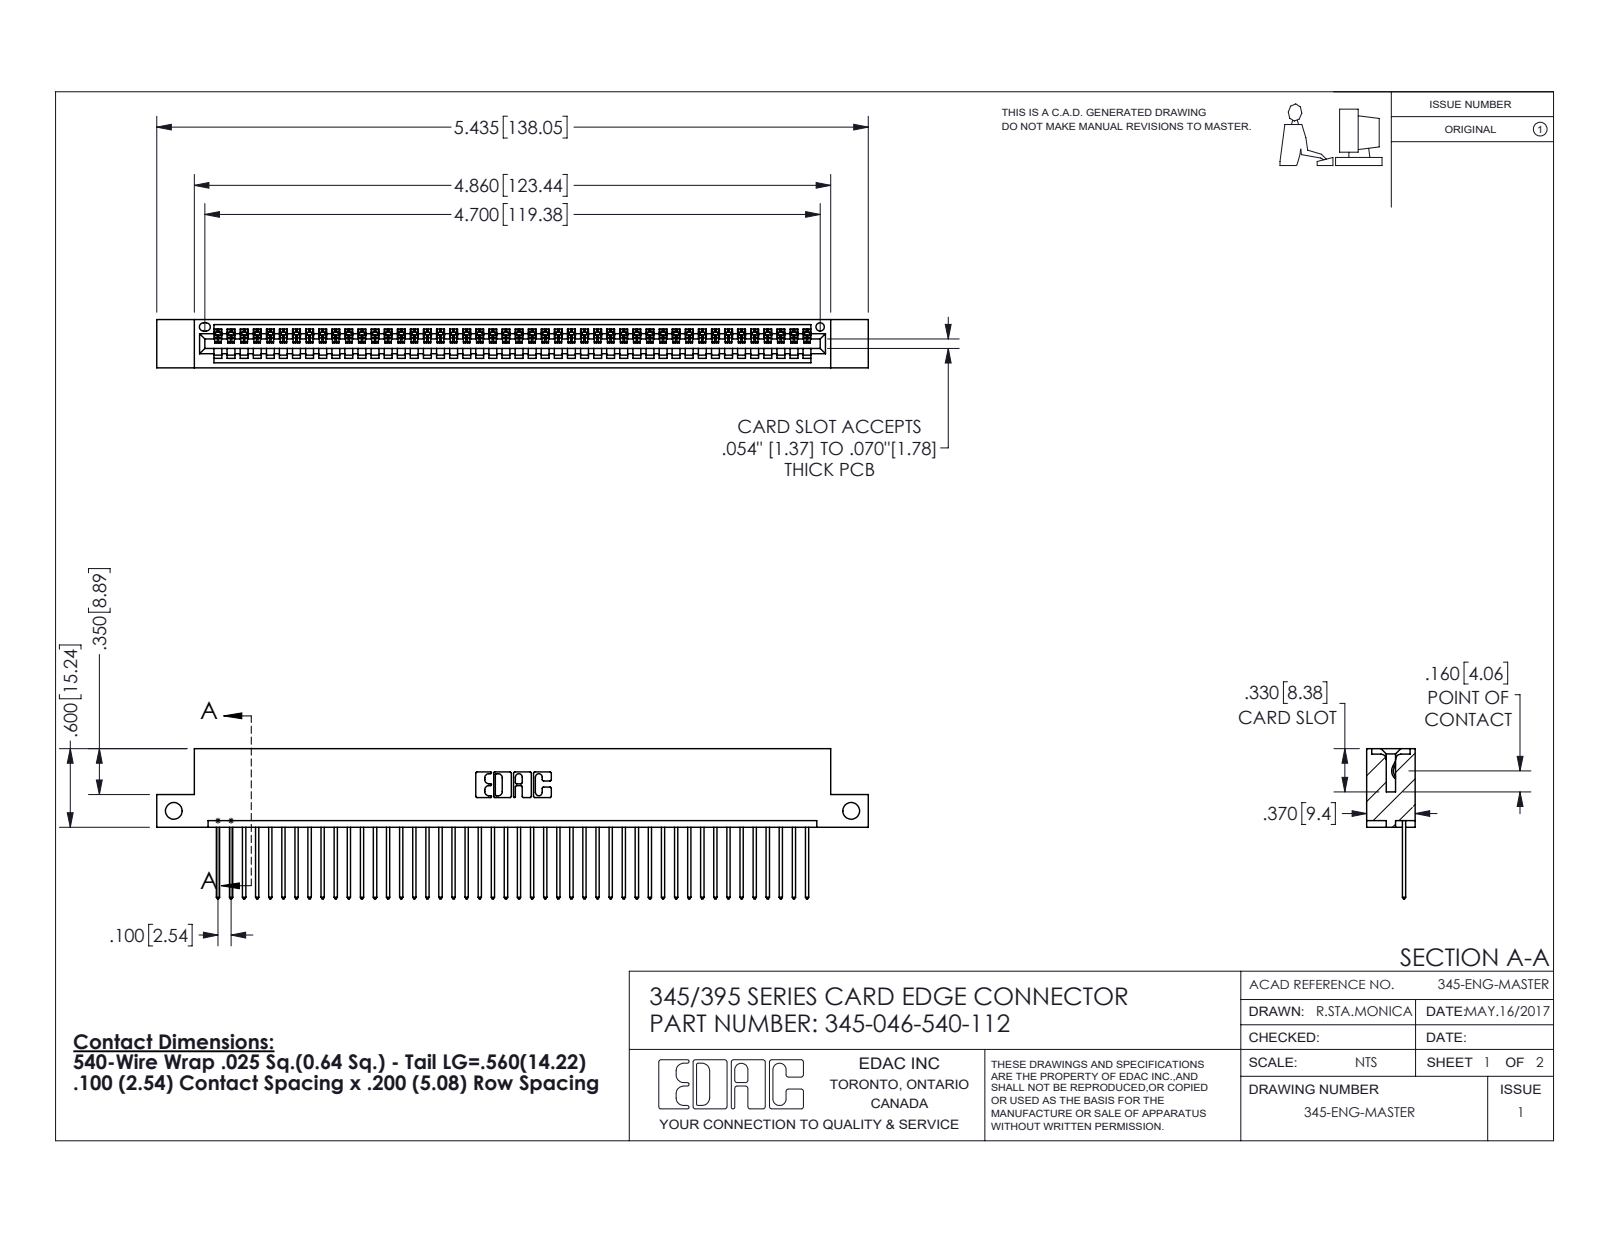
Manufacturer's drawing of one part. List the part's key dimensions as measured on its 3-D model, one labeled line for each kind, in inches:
Part name (STEP PRODUCT): 345-292-001_345-293-140; 345-046-540-112; 345 Part_Flush Mounting Lugs - Side Mount
STEP written by: SolidWorks 2016 (CONFIG_CONTROL_DESIGN)
Units: inches
Bodies: 47 solids, 2794 faces (1920 planar, 874 cylindrical, 0 other)
Overall size (bounding box): 5.435 × 1.147 × 0.37
Volume: 0.801 in³ · Surface area: 27.58 in²
Round holes (diameter × count): ⌀0.128 ×2, ⌀0.064 ×1
Partial cylindrical surfaces — rounded edges, fillets, slot ends (radius × count): R0.006 ×92, R0.01 ×92, R0.01 ×22, R0.007 ×6, R0.031 ×6, R0.026 ×3, R0.031 ×2, R0.04 ×2
Main face-to-face distances: 0.298, 0.072, 0.37, 0.2, 0.098, 0.272, 0.025, 0.225, 0.149, 0.072
Hole centre spacings: 5.175
